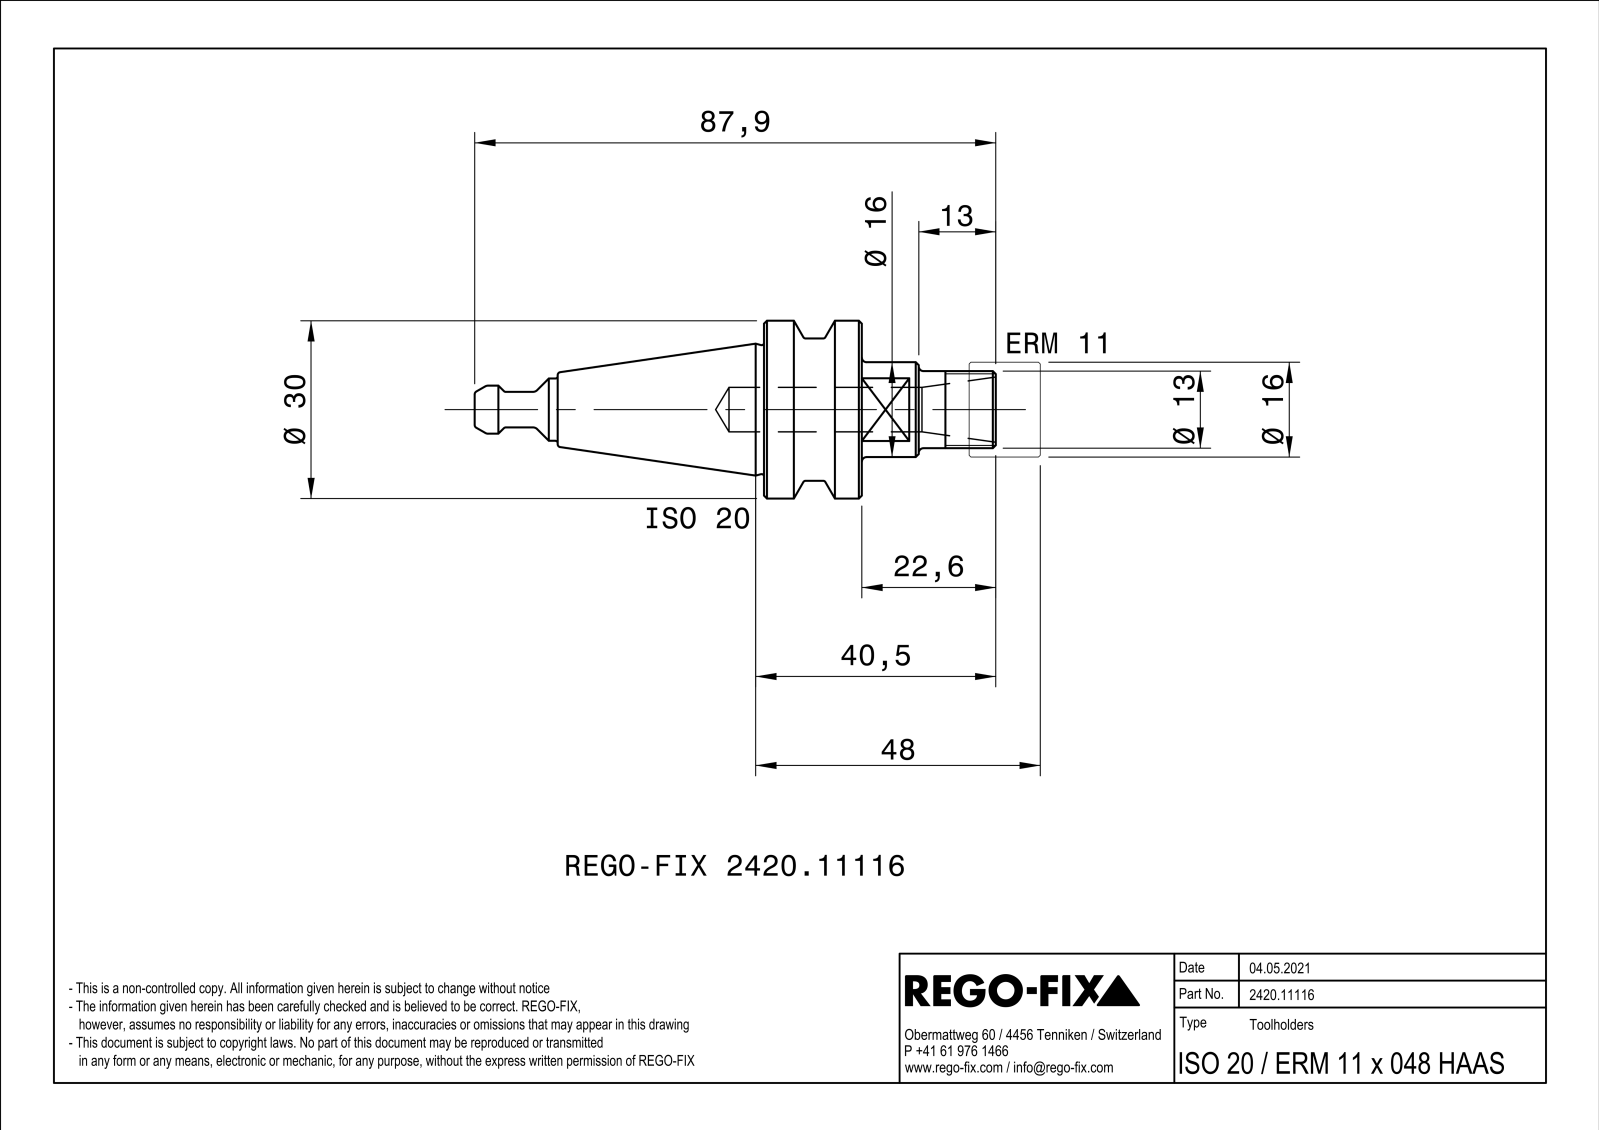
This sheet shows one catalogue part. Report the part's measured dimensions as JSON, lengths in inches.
{"part_name": "NOCUT", "step_written_by": "SIEMENS PLM Software Solid Edge ST10 (AUTOMOTIVE_DESIGN)", "units": "inches", "bodies": {"solids": 1, "faces": 46, "planar": 10, "cylindrical": 10, "other": 26}, "overall_size": [3.461, 1.181, 1.181], "volume_in3": 1.263, "surface_area_in2": 11.1, "round_holes": [[0.295, 1]], "round_bosses_or_shafts": [[1.181, 1], [0.945, 1], [0.63, 1], [0.512, 1], [0.413, 1], [0.319, 1], [0.236, 1]], "face_to_face_distances": [0.65, 0.472, 0.315, 0.965, 2.886, 2.571, 1.921, 0.063, 0.378, 1.028]}
